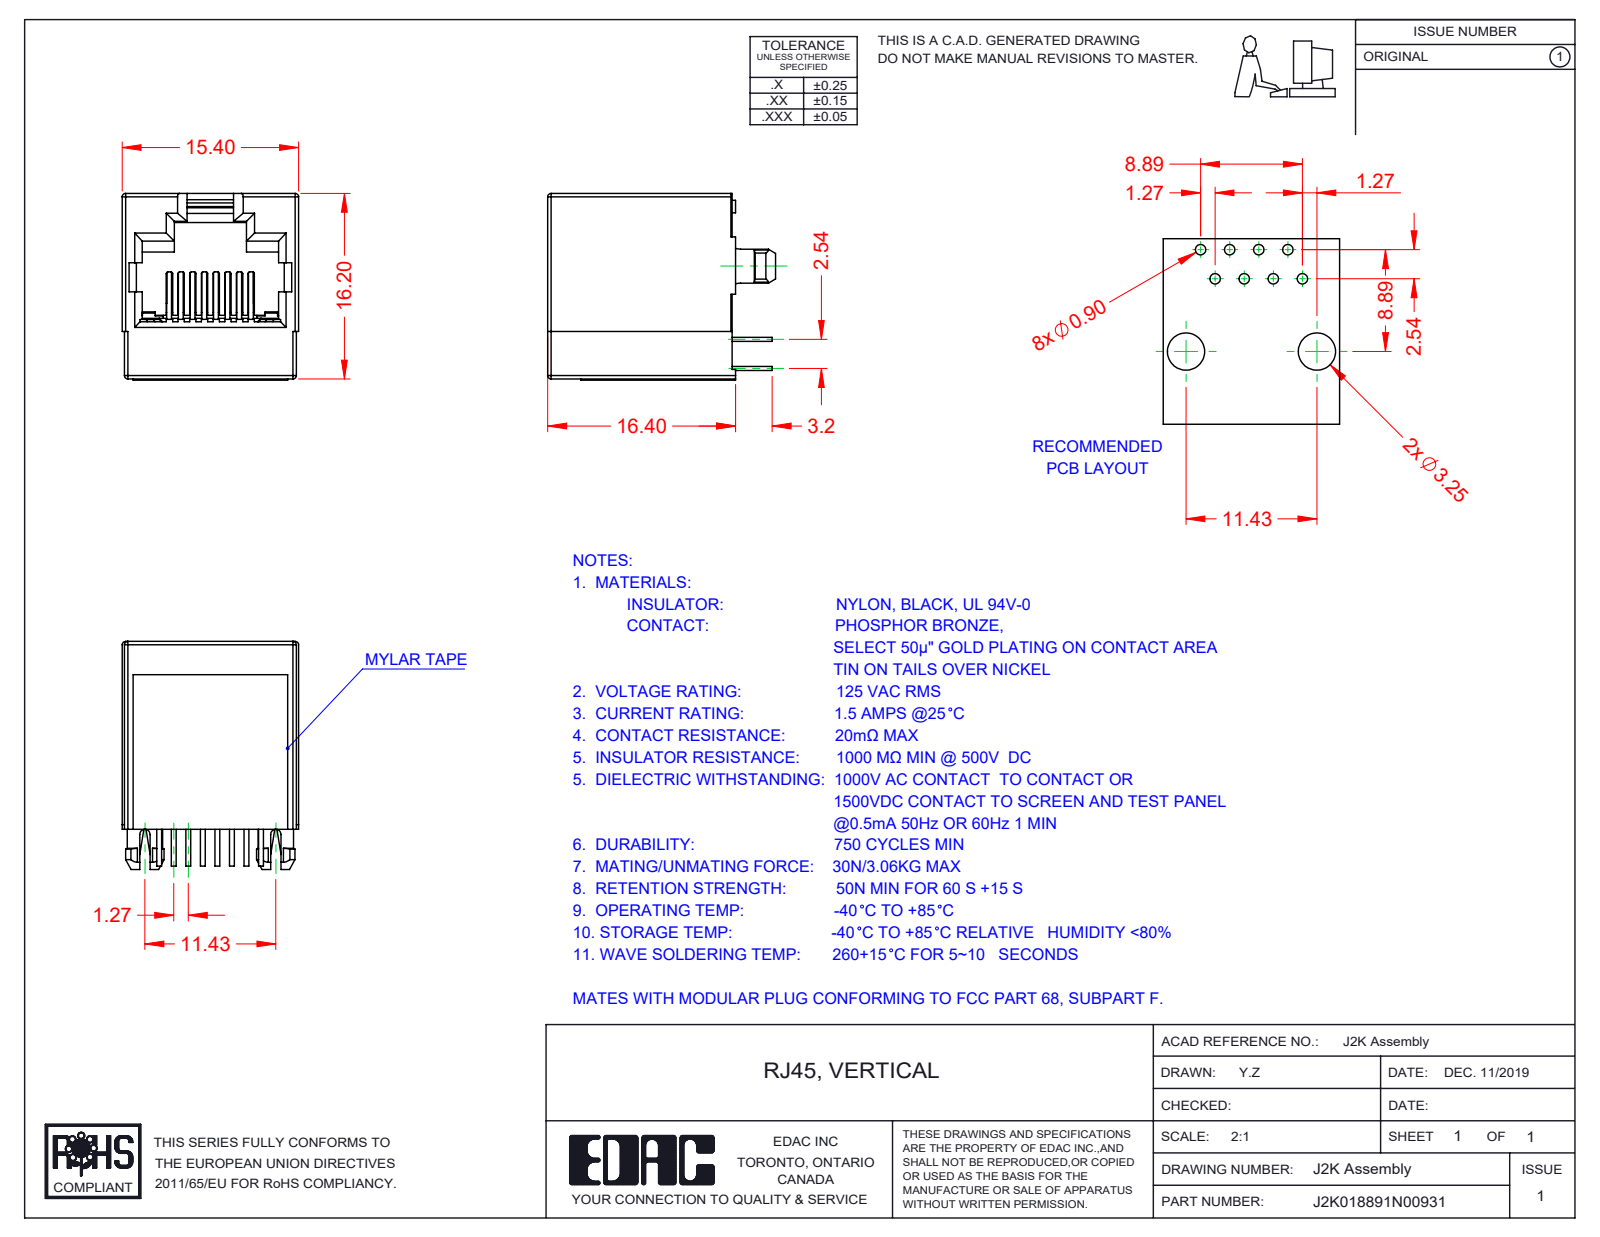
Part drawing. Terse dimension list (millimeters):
name: 2K Insulator; RJ2K018891N00931; 2K Contacts; 2K Mylar Tape (+1 more)
written by: SolidWorks 2016 (CONFIG_CONTROL_DESIGN)
unit: mm
bodies: 11 solids, 729 faces (592 planar, 113 cylindrical, 24 other)
size: 19.9 × 16.3 × 15.4
volume: 2 491 mm³; area: 4 332 mm²
bosses: 2× ⌀3.1, 2× ⌀1.1
rounds: 16× R0.15, 10× R0.3, 3× R0.5, 2× R0.1, 2× R0.2, 2× R0.45, 2× R0.6, 2× R0.95
face distances: 16.2, 15.4, 16.3, 14, 1.4, 1.2, 13.8, 15.2, 0.5, 1.3
